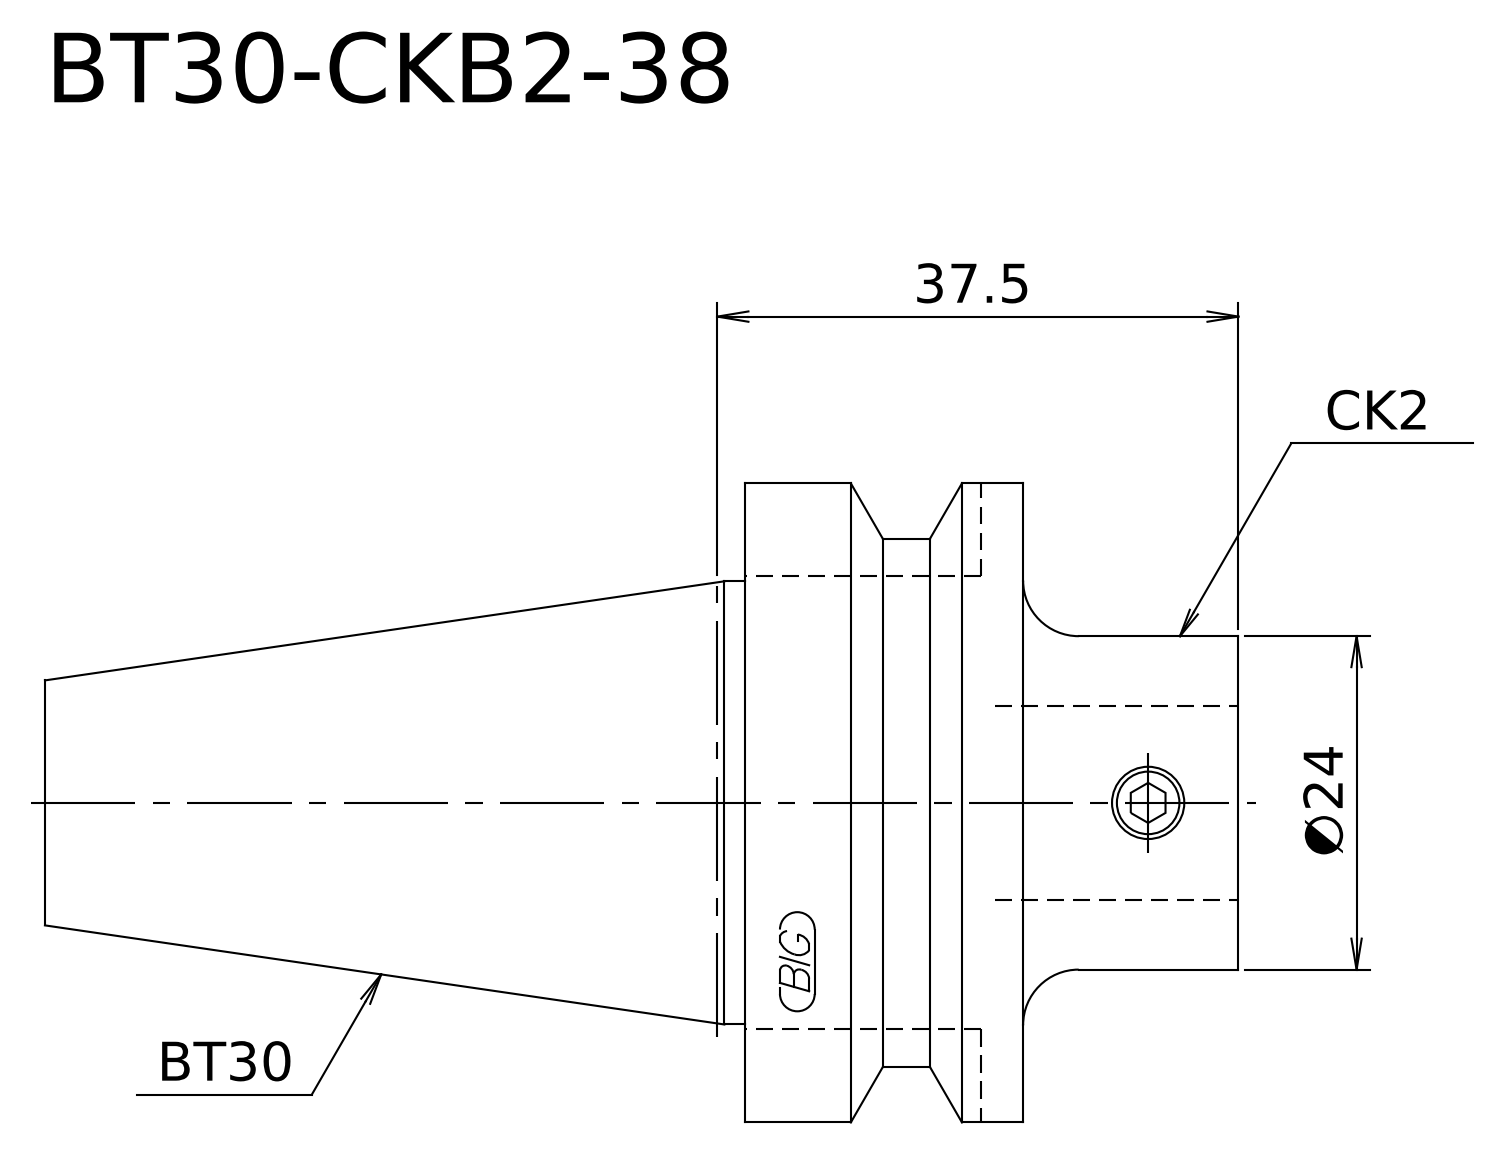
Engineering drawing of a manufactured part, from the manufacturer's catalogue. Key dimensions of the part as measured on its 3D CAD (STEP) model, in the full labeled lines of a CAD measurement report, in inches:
STEP written by: Kubotek KeyCreator V8.5.1 (14335) (CONFIG_CONTROL_DESIGN)
Units: inches
Bodies: 1 solid, 13 faces (4 planar, 5 cylindrical, 4 other)
Overall size (bounding box): 3.382 × 1.811 × 1.811
Volume: 3.886 in³ · Surface area: 17.21 in²
Round bosses / shafts (diameter × count): ⌀1.811 ×1, ⌀1.496 ×1, ⌀1.256 ×1, ⌀0.945 ×1
Main face-to-face distances: 0.787, 0.61, 1.398, 3.382, 2.772, 1.984
